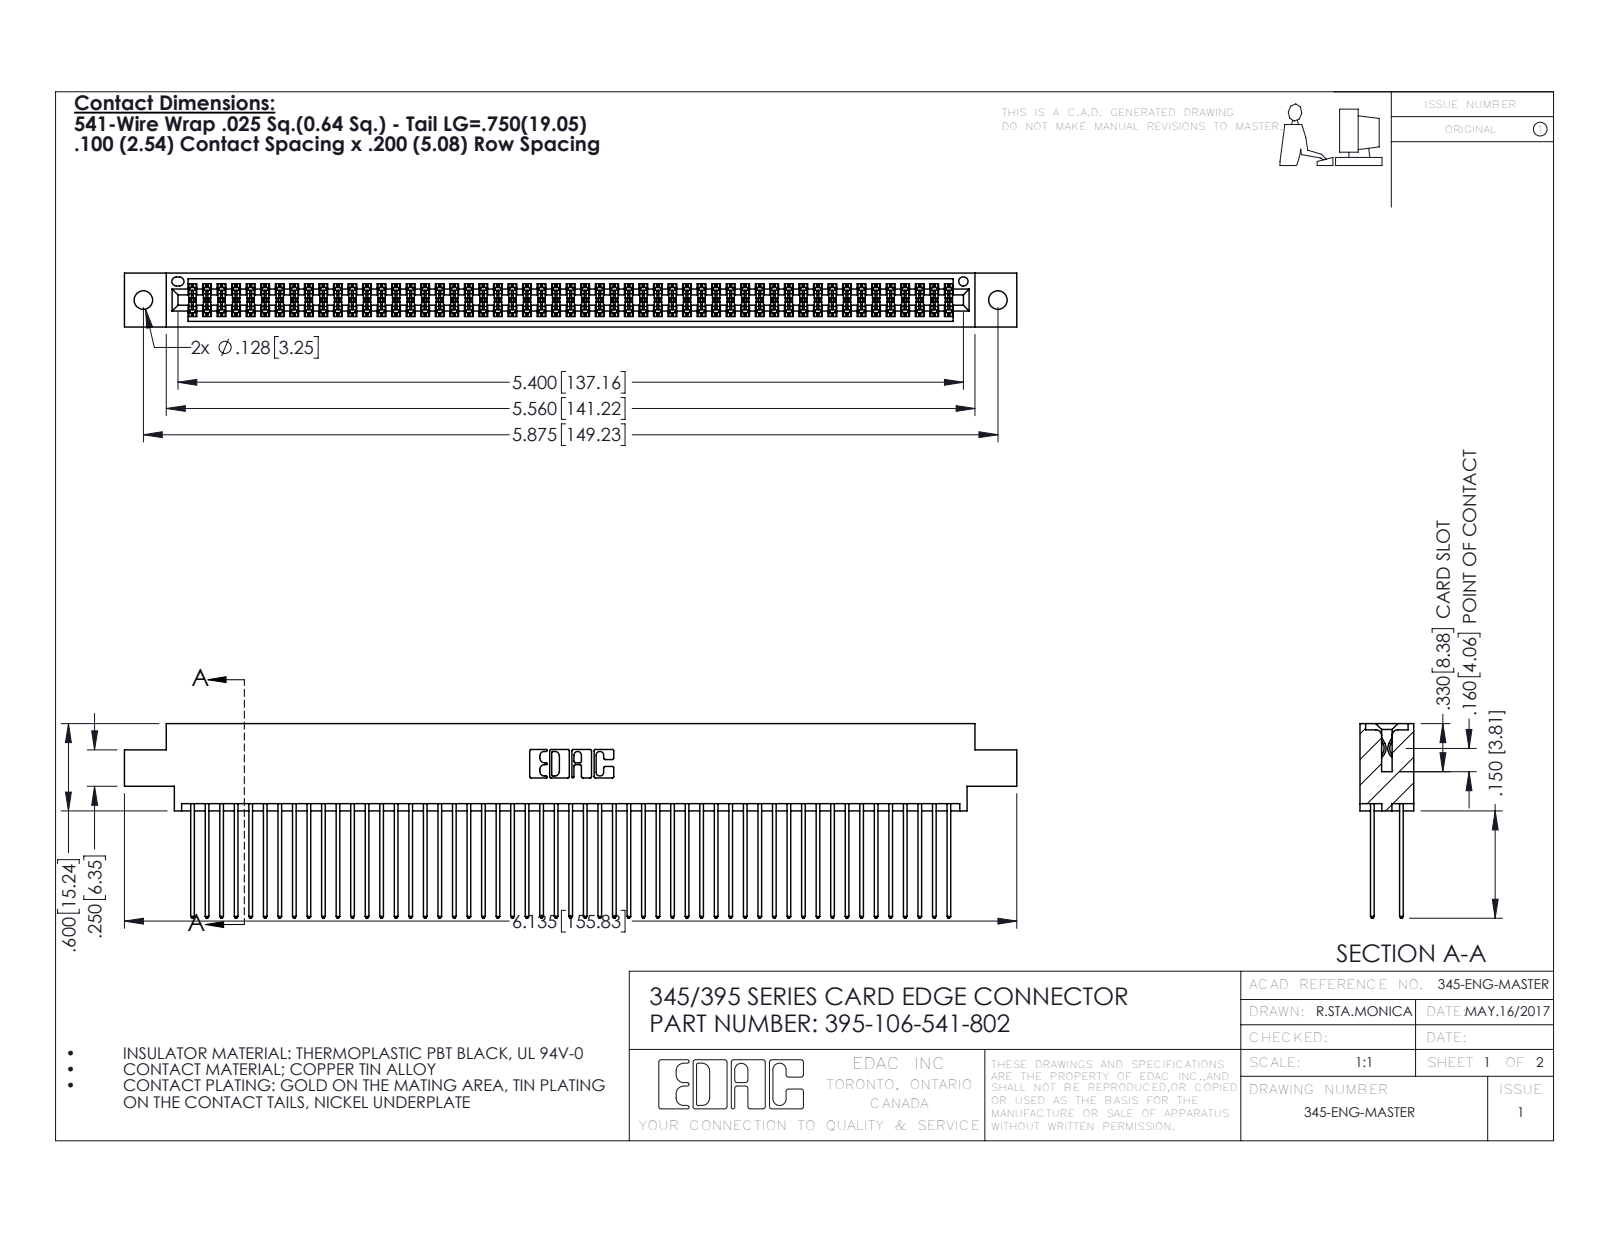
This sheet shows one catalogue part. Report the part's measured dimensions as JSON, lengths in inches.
{"part_name": "345 Part_0.170 Offset - 0.128 Dia; 395-106-541-802; 345-292-001_345-293-141", "step_written_by": "SolidWorks 2016 (CONFIG_CONTROL_DESIGN)", "units": "inches", "bodies": {"solids": 107, "faces": 5430, "planar": 3582, "cylindrical": 1848, "other": 0}, "overall_size": [6.135, 1.337, 0.37], "volume_in3": 0.958, "surface_area_in2": 40.53, "round_holes": [[0.128, 2], [0.064, 1]], "partial_cylinders_radius": [[0.006, 159], [0.01, 106], [0.01, 22], [0.007, 6], [0.031, 6], [0.026, 3], [0.014, 2], [0.019, 2]], "face_to_face_distances": [0.298, 0.072, 0.2, 0.098, 0.272, 0.025, 0.225, 0.37, 0.175, 0.149], "hole_center_spacings": [0.27, 5.639, 5.875]}
